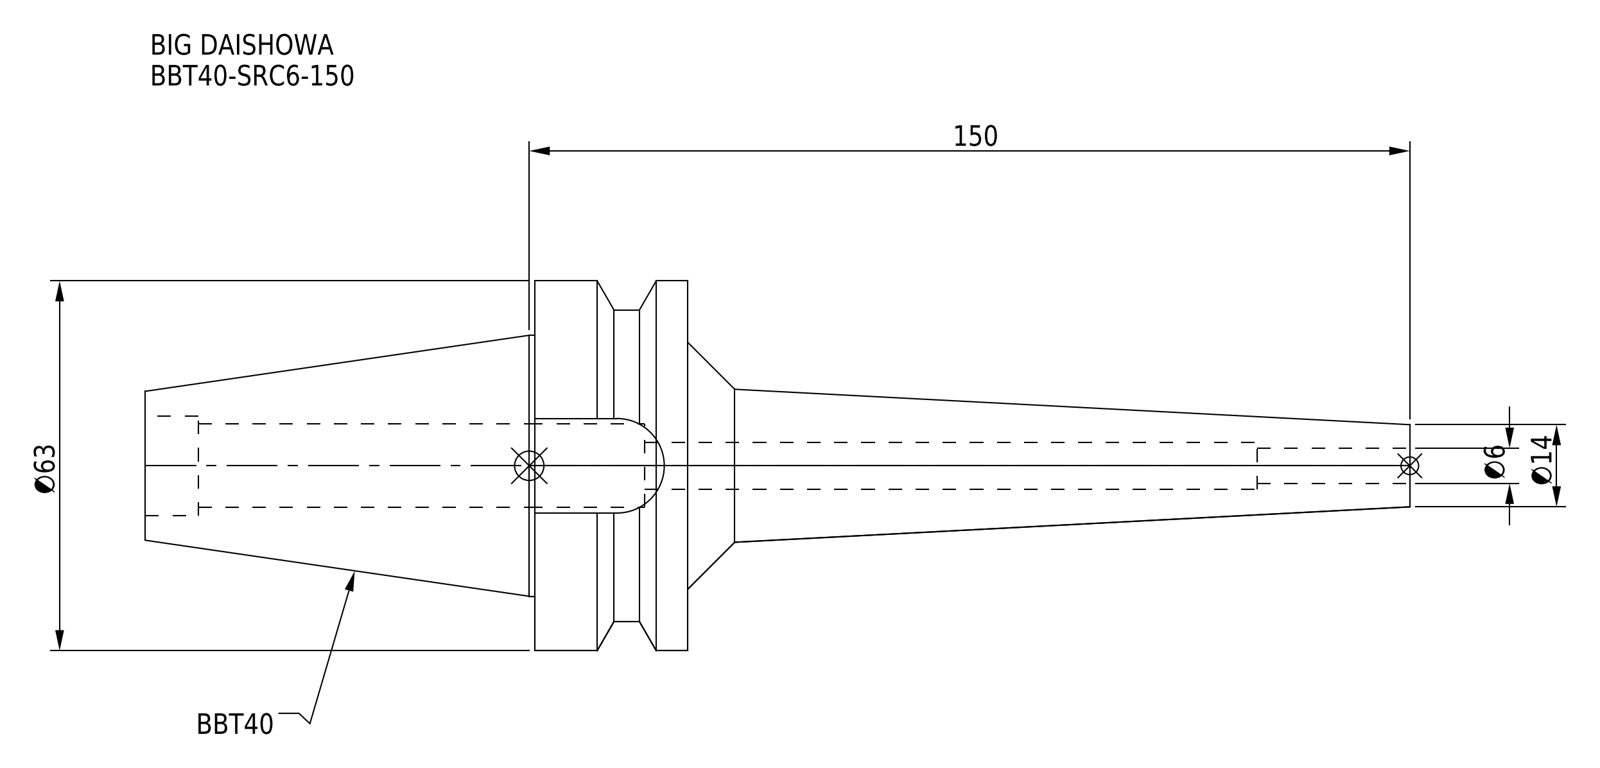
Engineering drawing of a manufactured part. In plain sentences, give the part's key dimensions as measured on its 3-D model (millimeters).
The part is named "BBT40-SRC6-150". Its 3-D file was written by "CREO PARAMETRIC BY PTC INC, 2016380 (AUTOMOTIVE_DESIGN)". It is 1 solid with 43 faces: 13 planar, 20 cylindrical and 10 other. Overall it measures 215.4 by 63 by 63 millimeters. Its volume is 160 257 cubic millimeters and its surface area 32 961 square millimeters. Round holes: 1 of diameter 6, 1 of diameter 8, 1 of diameter 14.2, 1 of diameter 17. Round bosses or shafts: 1 of diameter 63, 1 of diameter 53, 1 of diameter 44.45. Partial cylindrical surfaces (rounded edges, fillets, slot ends): 1 of radius 8.05. The main face-to-face distances are 26, 45, 92.4, 66.4, 16.1, 123, 149, 215.4, 130.4, 7.4.
